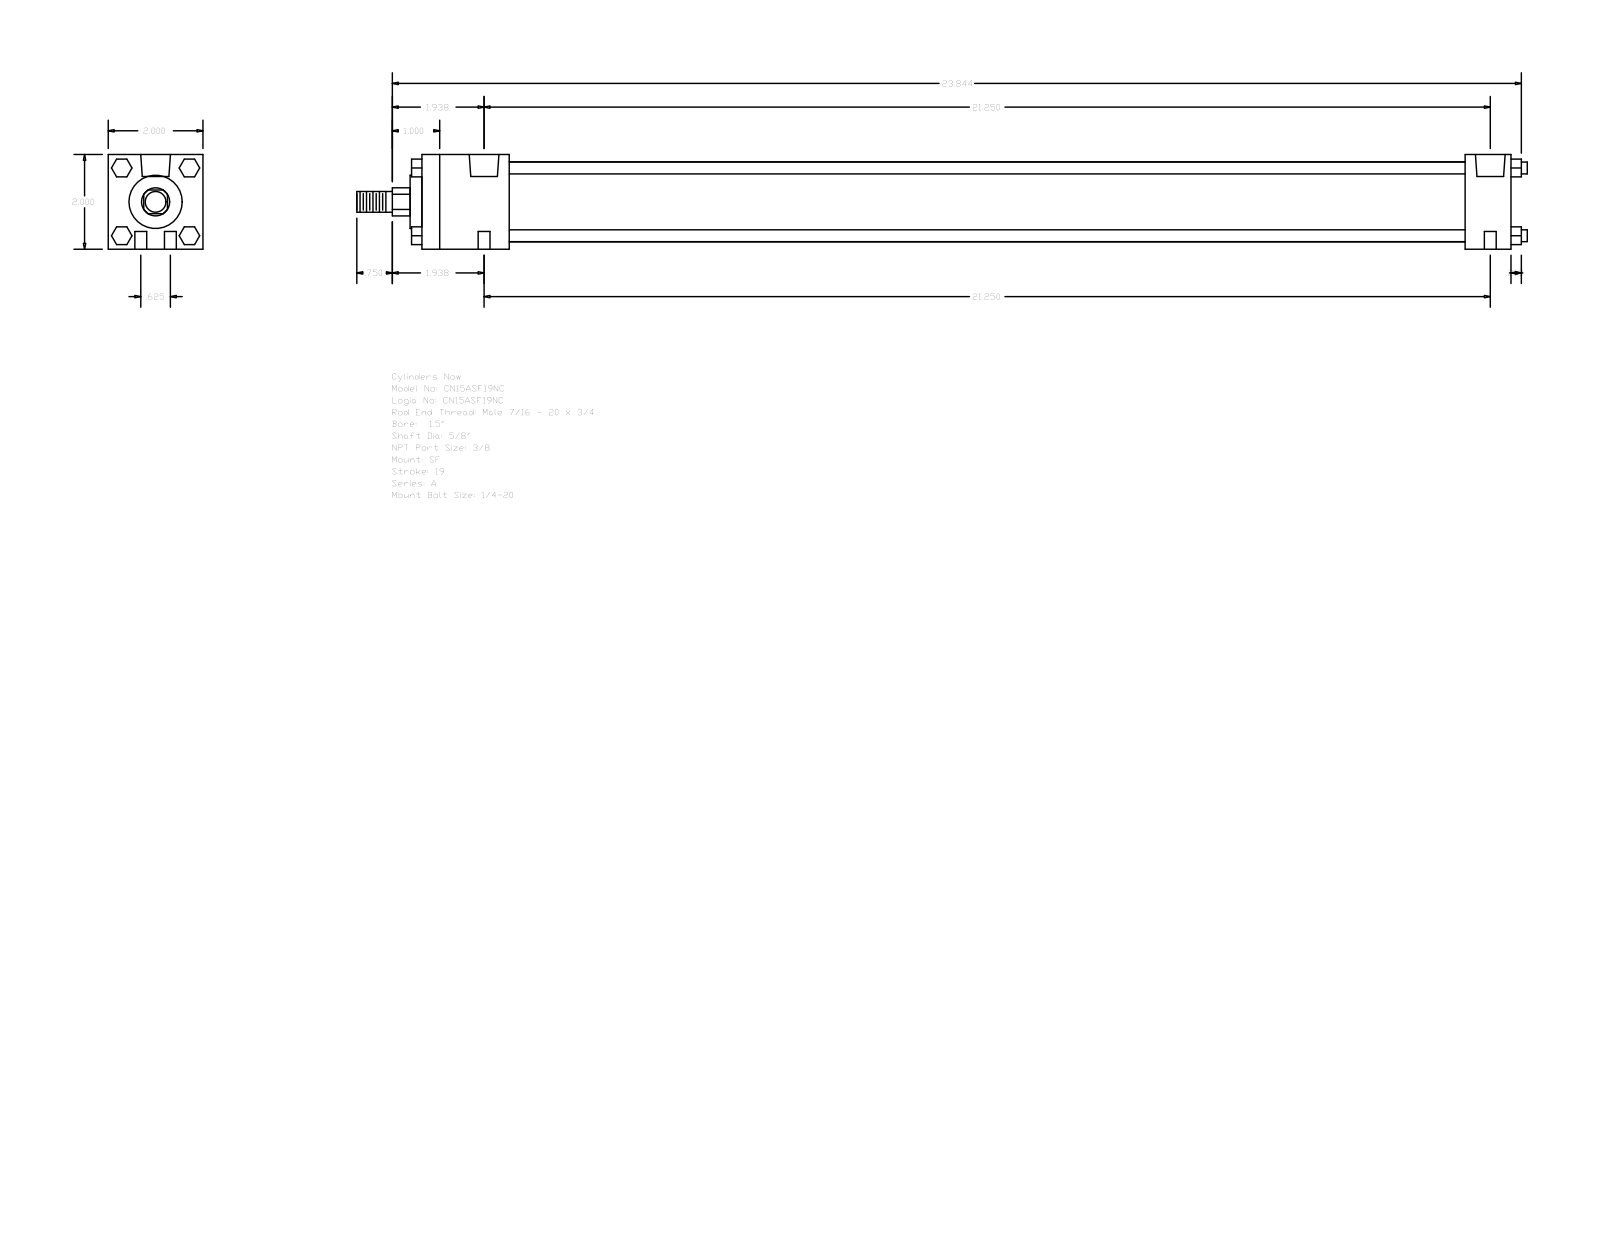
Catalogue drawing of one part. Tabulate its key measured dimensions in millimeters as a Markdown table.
| quantity | value |
| --- | --- |
| part name | A_SF__0150_0.625 |
| STEP written by | GSSL Pune (CONFIG_CONTROL_DESIGN) |
| units | millimeters |
| bodies | 0 solids, 124 faces (94 planar, 30 cylindrical, 0 other) |
| overall size | 627.86 × 50.8 × 50.8 |
| round holes (diameter × count) | 6.35 × 4, 5.56 × 2, 15.93 × 2 |
| round bosses / shafts (diameter × count) | 6.35 × 4, 42.93 × 1, 28.57 × 1, 15.88 × 1, 11.11 × 1 |
| partial cylindrical surfaces (radius × count) | 7.54 × 1 |
| main face-to-face distances | 50.8, 584.2, 46.83, 559.59, 512.76, 537.37, 24.61, 6.35, 9.52, 53.18 |
| hole center spacings | 7.94, 539.81, 539.75, 15.88, 539.98, 531.81 |
